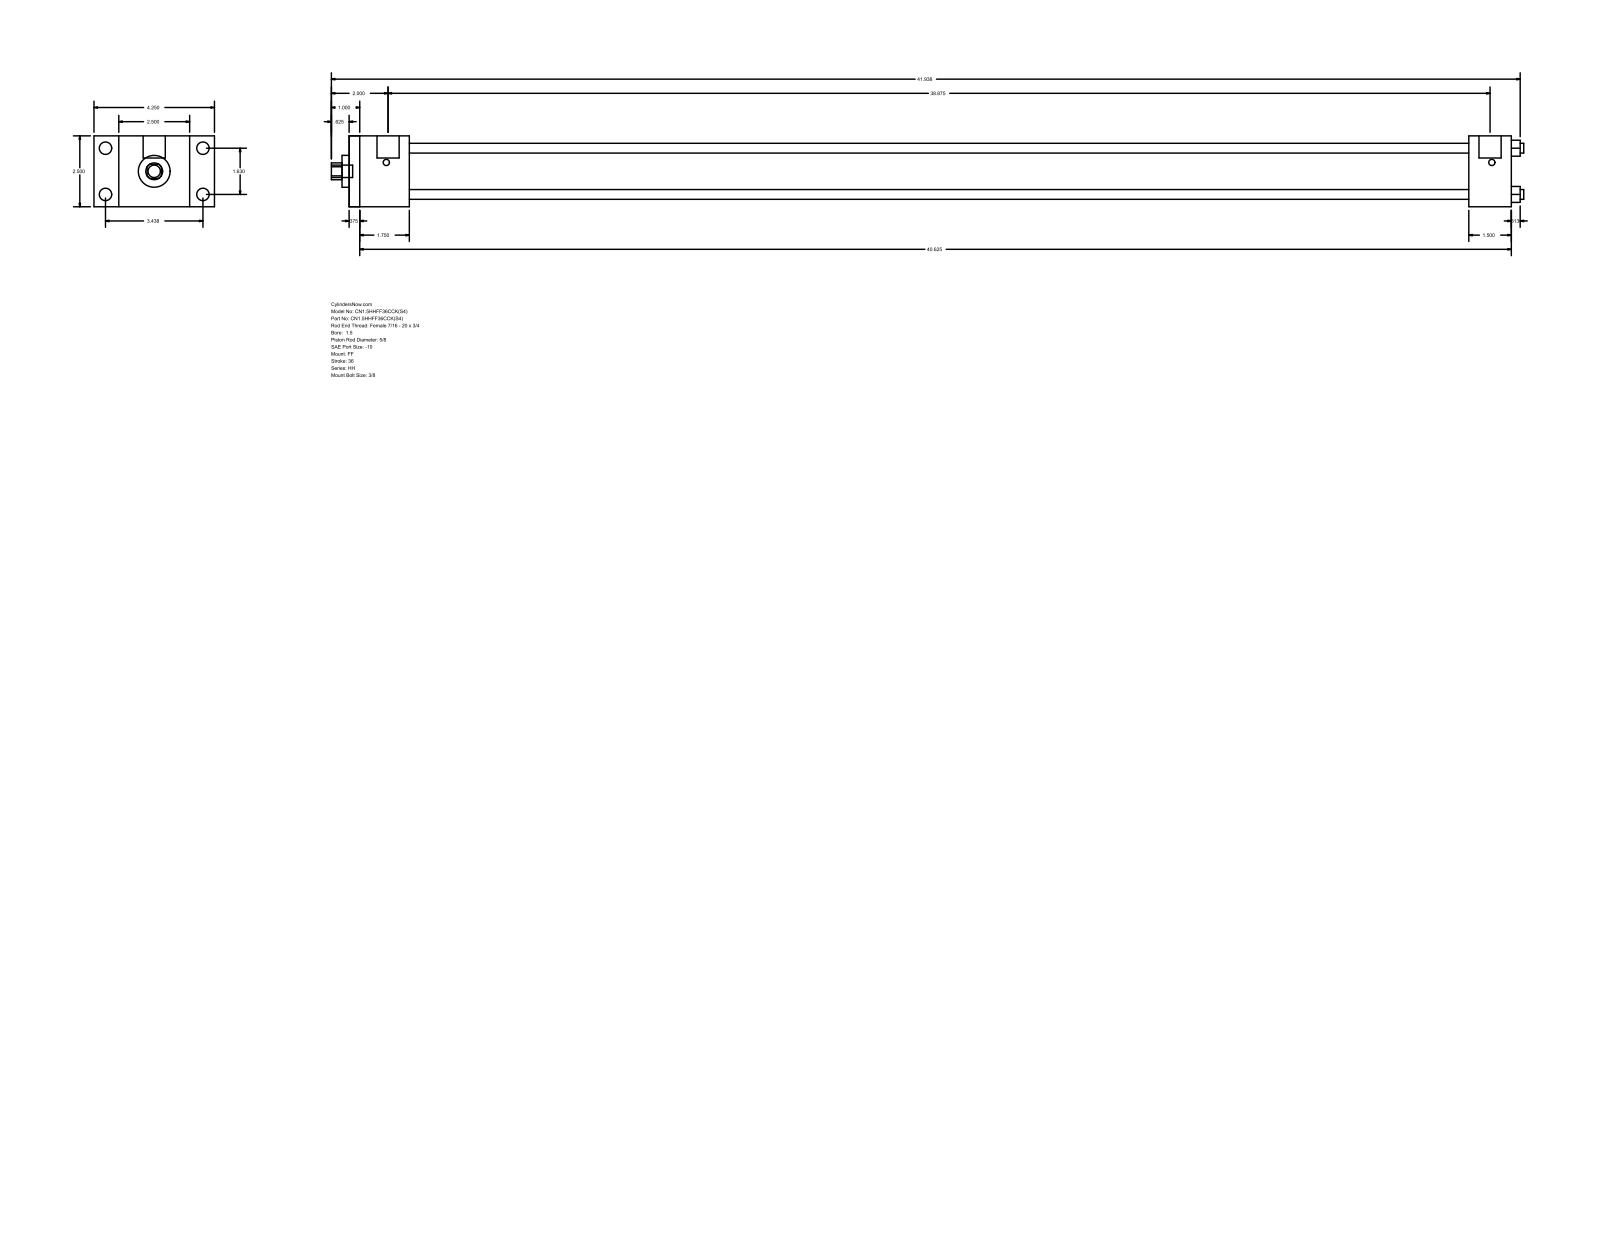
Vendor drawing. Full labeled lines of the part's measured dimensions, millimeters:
Part name (STEP PRODUCT): HH_FF__0150_0.625
STEP written by: GSSL Pune (CONFIG_CONTROL_DESIGN)
Units: millimetres
Bodies: 0 solids, 92 faces (64 planar, 28 cylindrical, 0 other)
Overall size (bounding box): 1068.39 × 107.95 × 63.5
Round holes (diameter × count): ⌀8.76 ×4, ⌀15.88 ×1, ⌀28.57 ×1, ⌀44.45 ×1
Round bosses / shafts (diameter × count): ⌀11.13 ×4, ⌀5.56 ×4, ⌀19.84 ×2, ⌀11.11 ×1
Partial cylindrical surfaces — rounded edges, fillets, slot ends (radius × count): R7.54 ×1
Main face-to-face distances: 63.5, 1041.4, 9.52, 1031.88, 53.97, 44.45, 987.43, 1003.29, 993.77, 949.32
Hole centre spacings: 29.27, 41.4, 58.55
